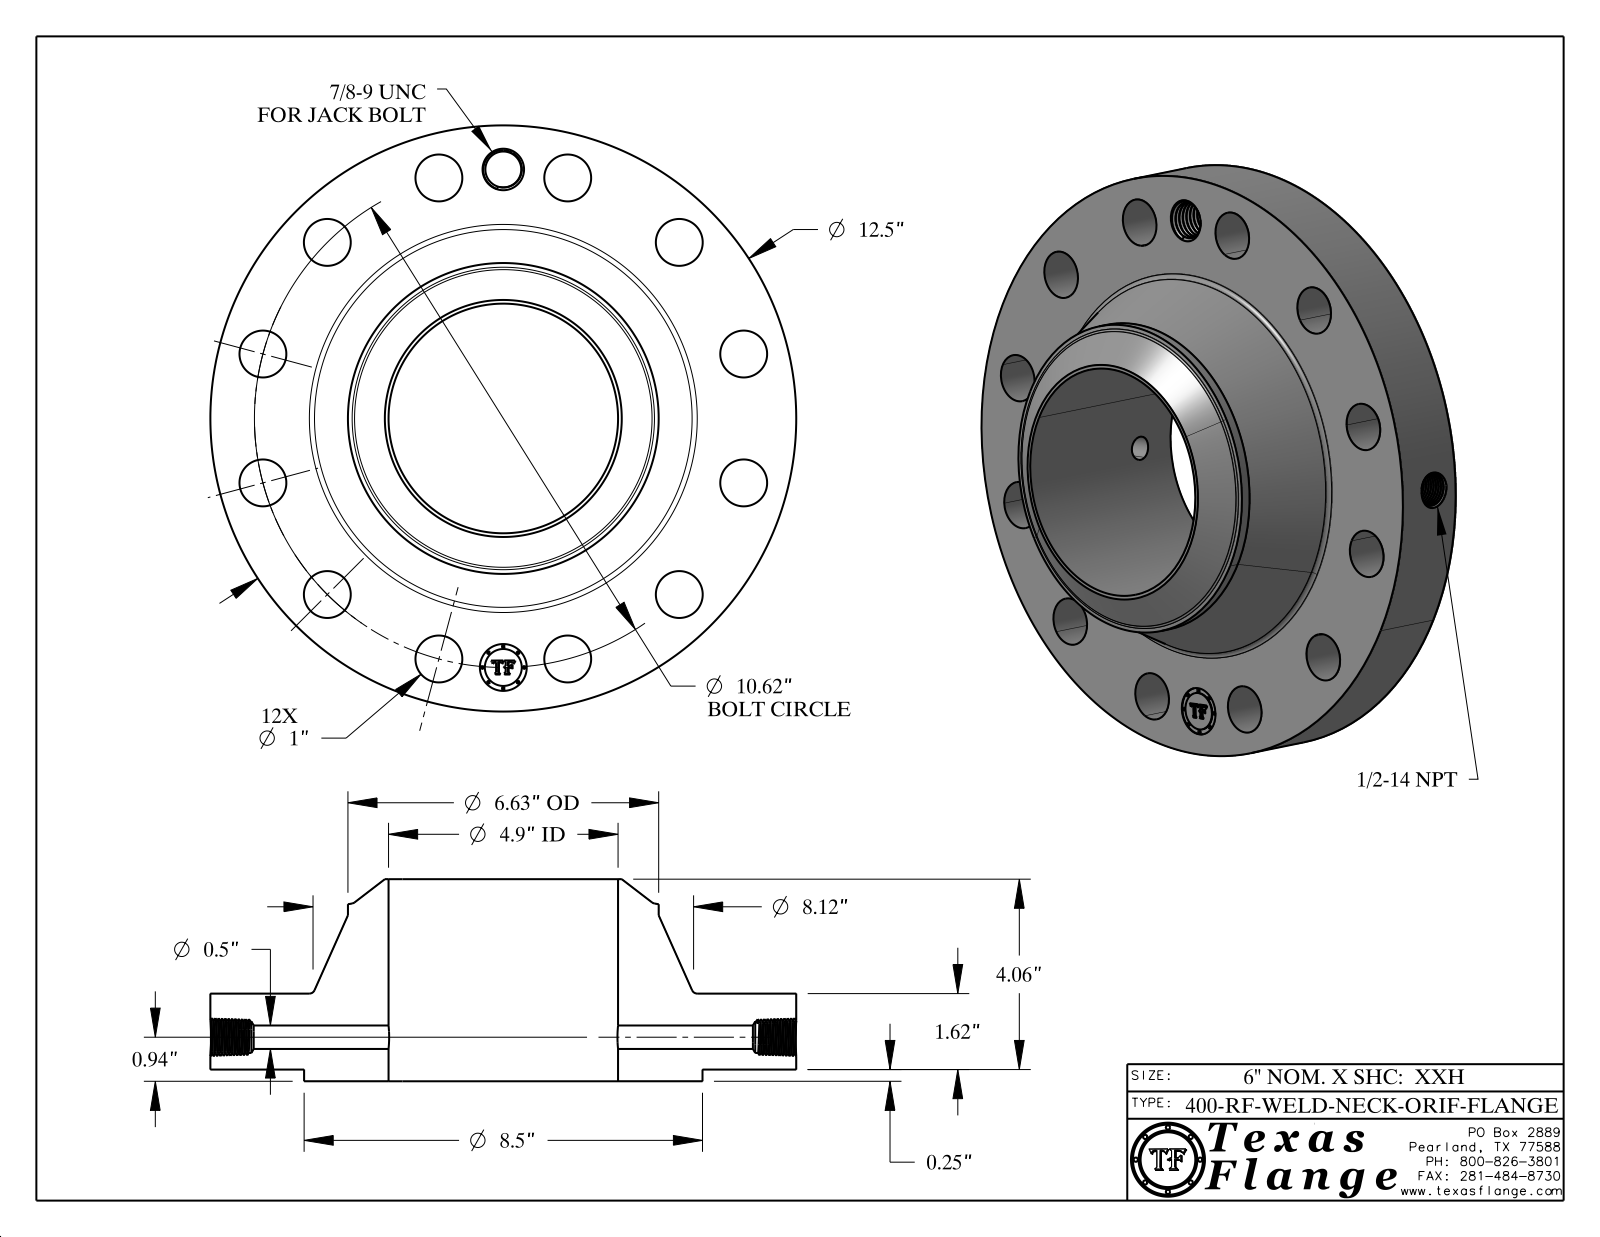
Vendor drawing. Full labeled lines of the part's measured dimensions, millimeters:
Part name (STEP PRODUCT): 400-RF-WELD-NECK
STEP written by: CATIA V5 STEP AP214 (AUTOMOTIVE_DESIGN)
Units: millimetres
Bodies: 1 solid, 777 faces (369 planar, 100 cylindrical, 308 other)
Overall size (bounding box): 317.5 × 317.5 × 109.5
Volume: 3 400 000 mm³ · Surface area: 283 500 mm²
Round holes (diameter × count): ⌀25.4 ×13, ⌀12.7 ×1, ⌀17.1 ×1, ⌀19.5 ×1, ⌀124.4 ×1
Round bosses / shafts (diameter × count): ⌀1.5 ×8, ⌀317.5 ×1, ⌀215.9 ×1, ⌀168.4 ×1, ⌀20 ×1
Main face-to-face distances: 41.1, 6.4, 47.5, 109.5, 103.1, 62, 0.4, 47.1, 40.8, 62.4
Hole centre spacings: 134.9, 190.7, 233.6, 260.6, 134.9, 69.8, 269.7, 35.2
